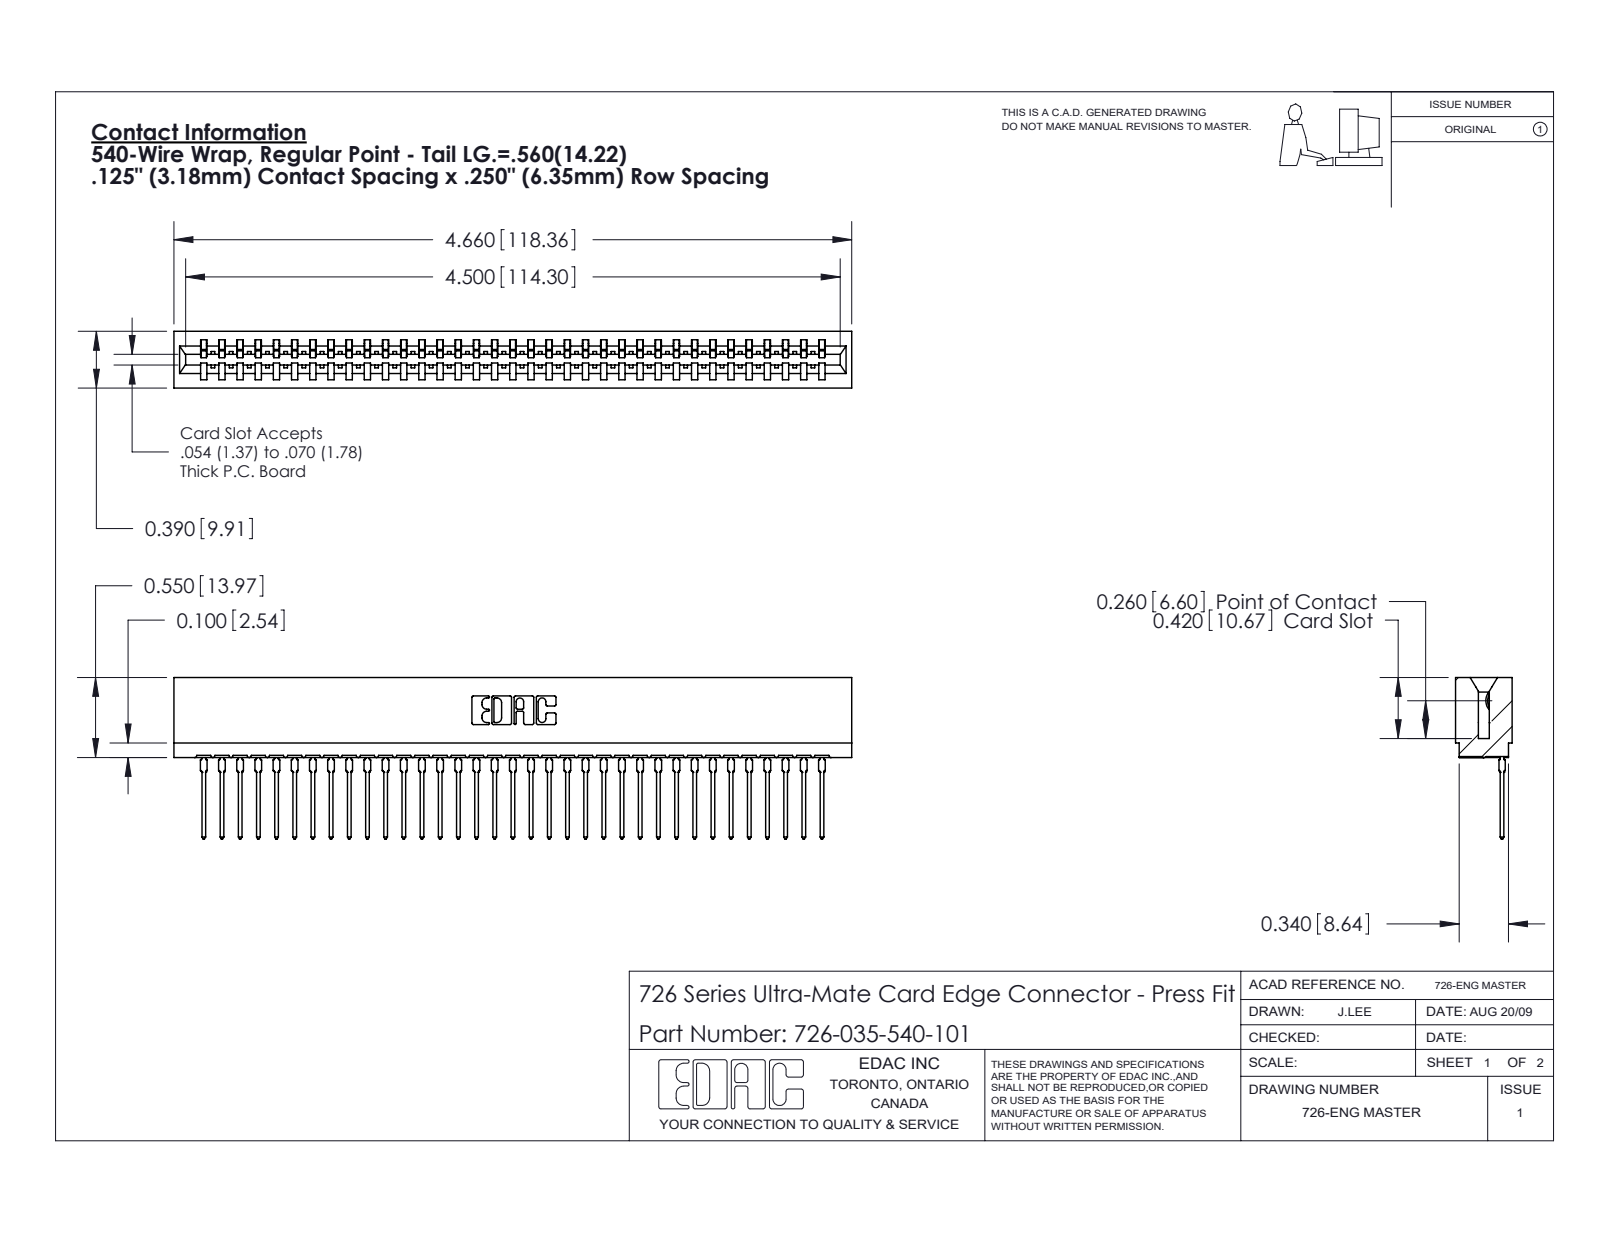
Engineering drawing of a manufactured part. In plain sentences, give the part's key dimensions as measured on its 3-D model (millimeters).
The part is named "746-292-001_540; 726-035-540-101; 726 Part_.515 Slot Depth - 01". Its 3-D file was written by "SolidWorks 2020 (CONFIG_CONTROL_DESIGN)". It is 36 solids with 3877 faces: 2260 planar, 707 cylindrical and 910 other. Overall it measures 118.4 by 28.2 by 9.9 millimeters. Its volume is 10 700 cubic millimeters and its surface area 16 630 square millimeters. Partial cylindrical surfaces (rounded edges, fillets, slot ends): 70 of radius 0.5, 36 of radius 0.4, 22 of radius 0.3, 6 of radius 0.2, 6 of radius 0.8, 4 of radius 0.1, 4 of radius 0.3, 3 of radius 0.7. The main face-to-face distances are 1.4, 8.5, 9.9, 6.4, 0.6, 7.8, 2.1, 12.7, 7, 9.3.
